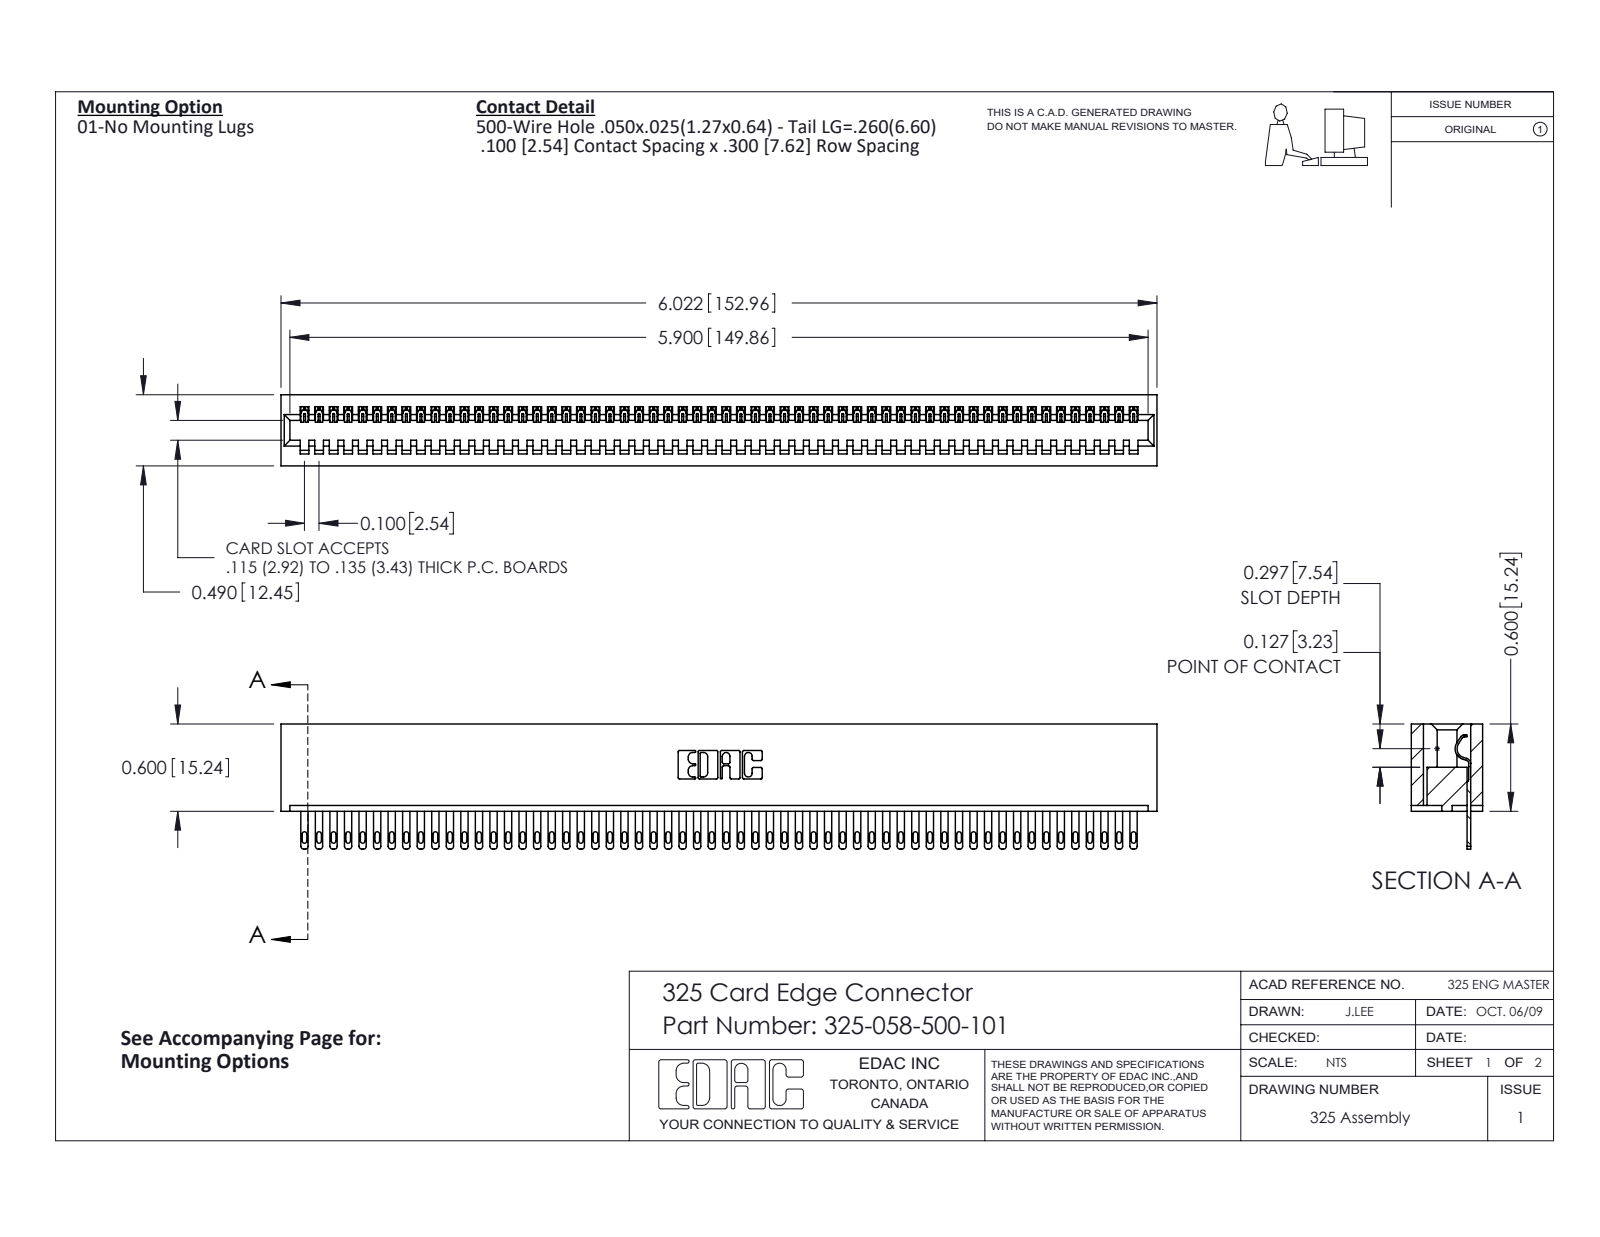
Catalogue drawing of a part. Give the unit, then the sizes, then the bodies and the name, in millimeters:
Units: millimetres
Overall size (bounding box): 153 × 21.8 × 12.4
Partial cylindrical surfaces — rounded edges, fillets, slot ends (radius × count): R0.2 ×116, R0.4 ×116, R0.5 ×116, R0.3 ×22, R0.2 ×6, R0.8 ×6, R0.7 ×3, R0.4 ×1
Main face-to-face distances: 2.1, 10.3, 12.4, 2.7, 9.7, 0.6, 7.6, 8.3, 6.7, 14.2
Volume: 20 160 mm³ · Surface area: 22 920 mm²
Bodies: 59 solids, 3238 faces (2154 planar, 1084 cylindrical, 0 other)
Part name (STEP PRODUCT): 325-058-500-101; 325 Part_Lugless; 325-292-001_325-293-100
STEP written by: SolidWorks 2016 (CONFIG_CONTROL_DESIGN)
